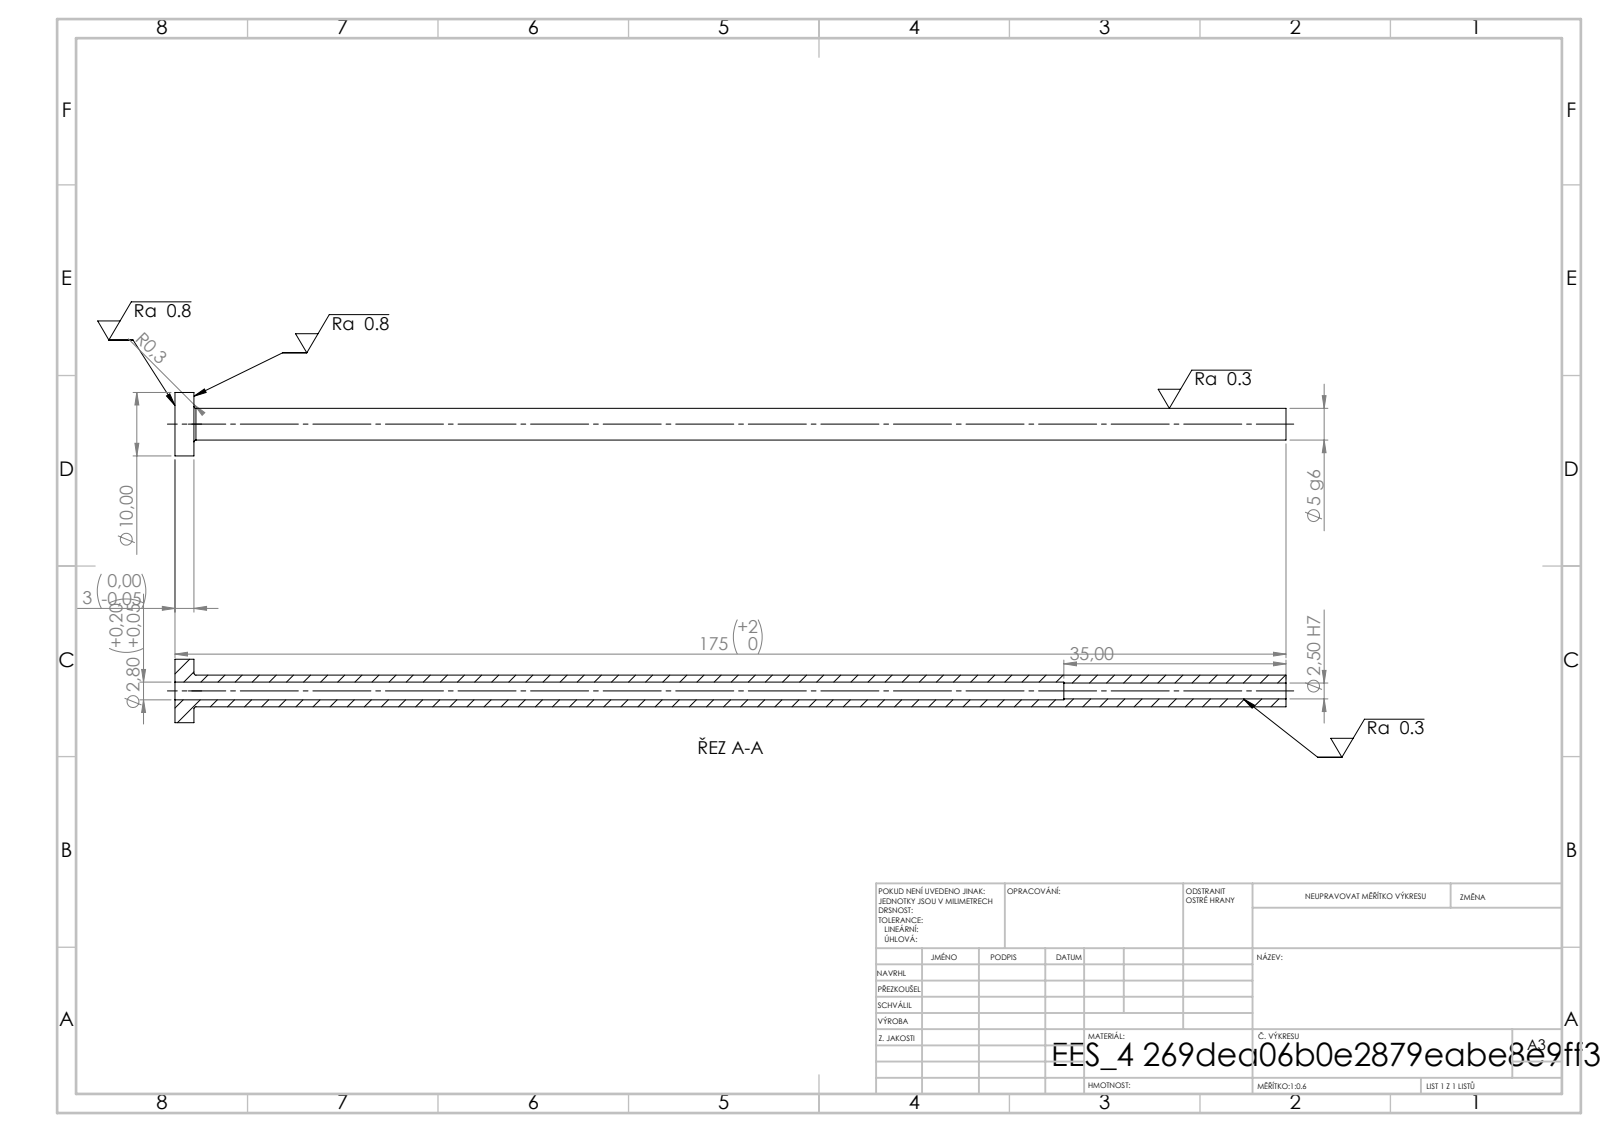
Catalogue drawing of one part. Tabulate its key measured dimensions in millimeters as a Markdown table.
| quantity | value |
| --- | --- |
| STEP written by | SolidWorks 2019 (CONFIG_CONTROL_DESIGN) |
| units | millimeters |
| bodies | 1 solid, 14 faces (4 planar, 8 cylindrical, 2 other) |
| overall size | 175 × 10 × 10 |
| volume | 2 579 mm³ |
| surface area | 4 448 mm² |
| round holes (diameter × count) | 2.5 × 1, 2.8 × 1 |
| round bosses / shafts (diameter × count) | 10 × 1, 5 × 1 |
| main face-to-face distances | 3, 175, 172, 140, 137, 35 |
